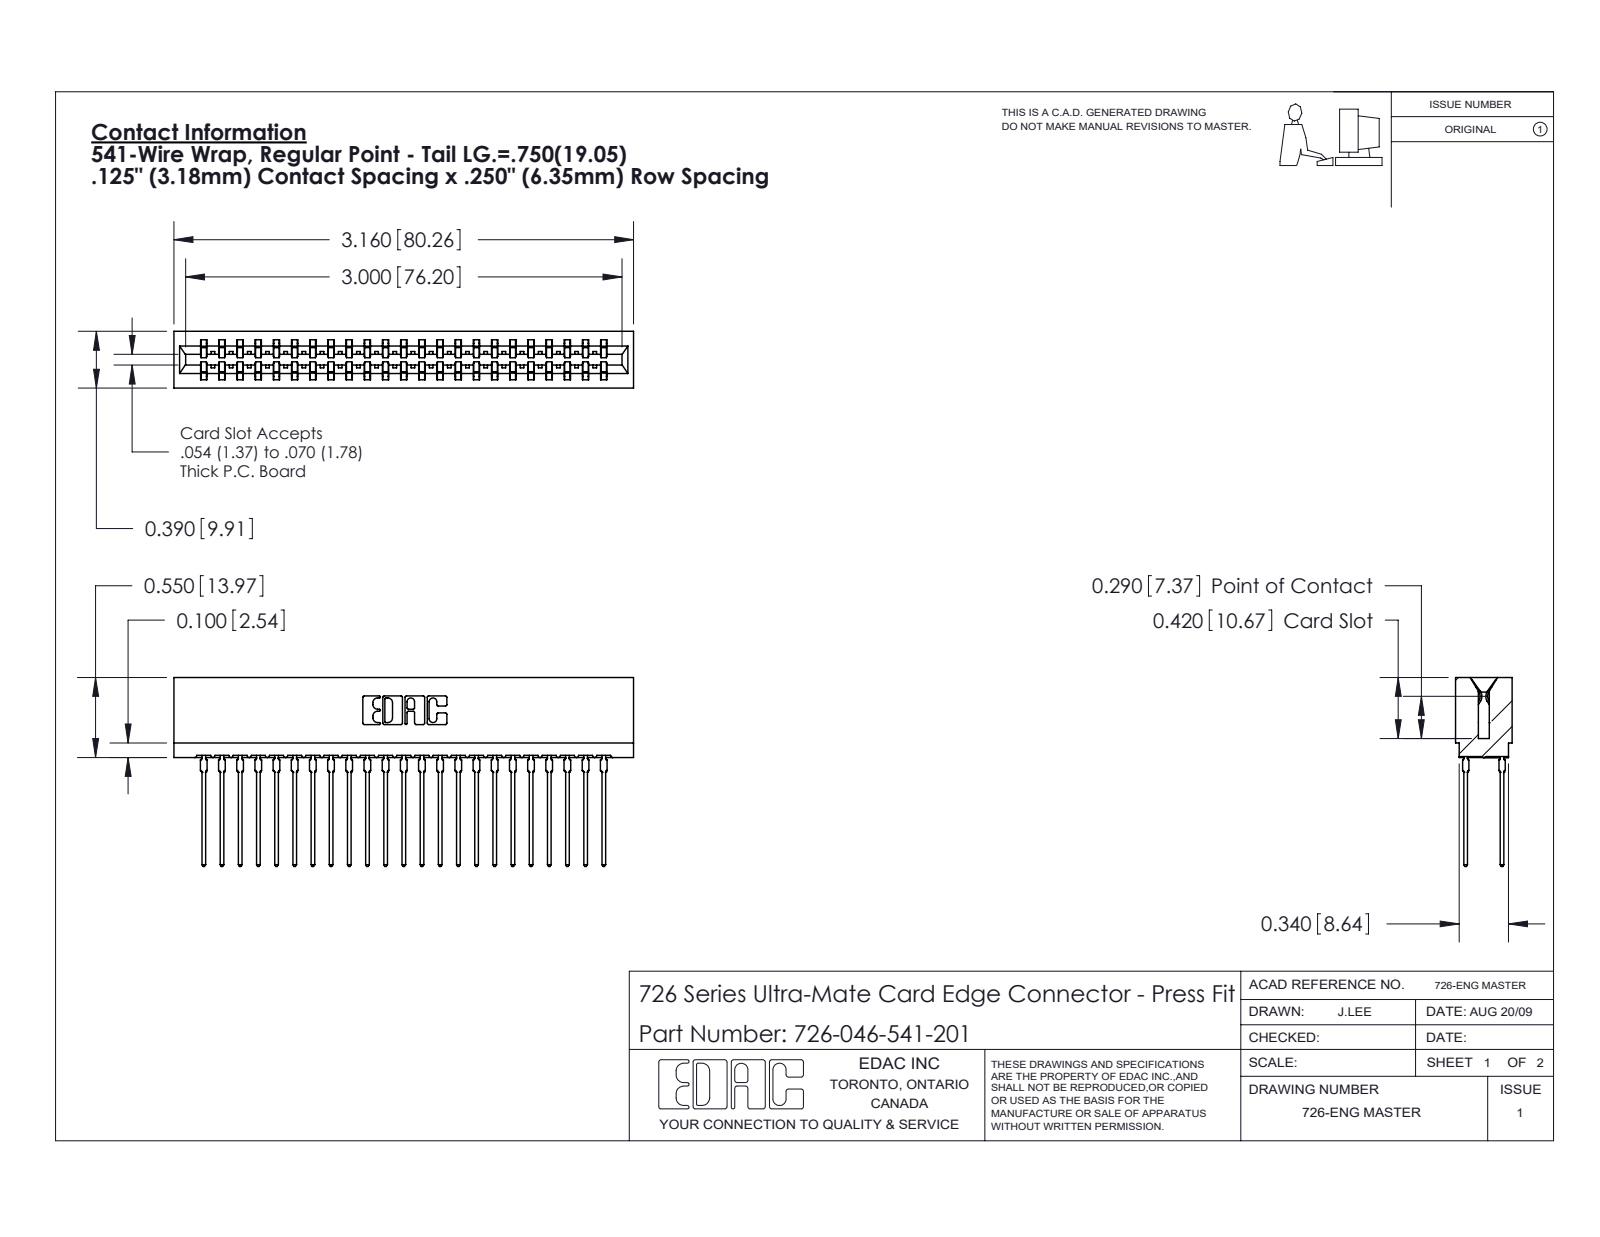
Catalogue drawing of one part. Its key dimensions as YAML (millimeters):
part_name: "726 Part_.515 Slot Depth - 01; 726-046-541-201; 746-292-001_541"
step_written_by: "SolidWorks 2020 (CONFIG_CONTROL_DESIGN)"
units: millimeters
bodies: {solids: 47, faces: 4214, planar: 2171, cylindrical: 847, other: 1196}
overall_size: [80.3, 33, 9.9]
volume: 7730
surface_area: 13740
partial_cylinders:
  - {radius: 0.5, count: 92}
  - {radius: 0.4, count: 24}
  - {radius: 0.3, count: 22}
  - {radius: 0.1, count: 8}
  - {radius: 0.3, count: 8}
  - {radius: 0.2, count: 6}
  - {radius: 0.8, count: 6}
  - {radius: 0.7, count: 3}
face_to_face_distances: [1.4, 8.5, 0.6, 7.8, 6.4, 2.1, 9.9, 7, 19.1, 1.1]
